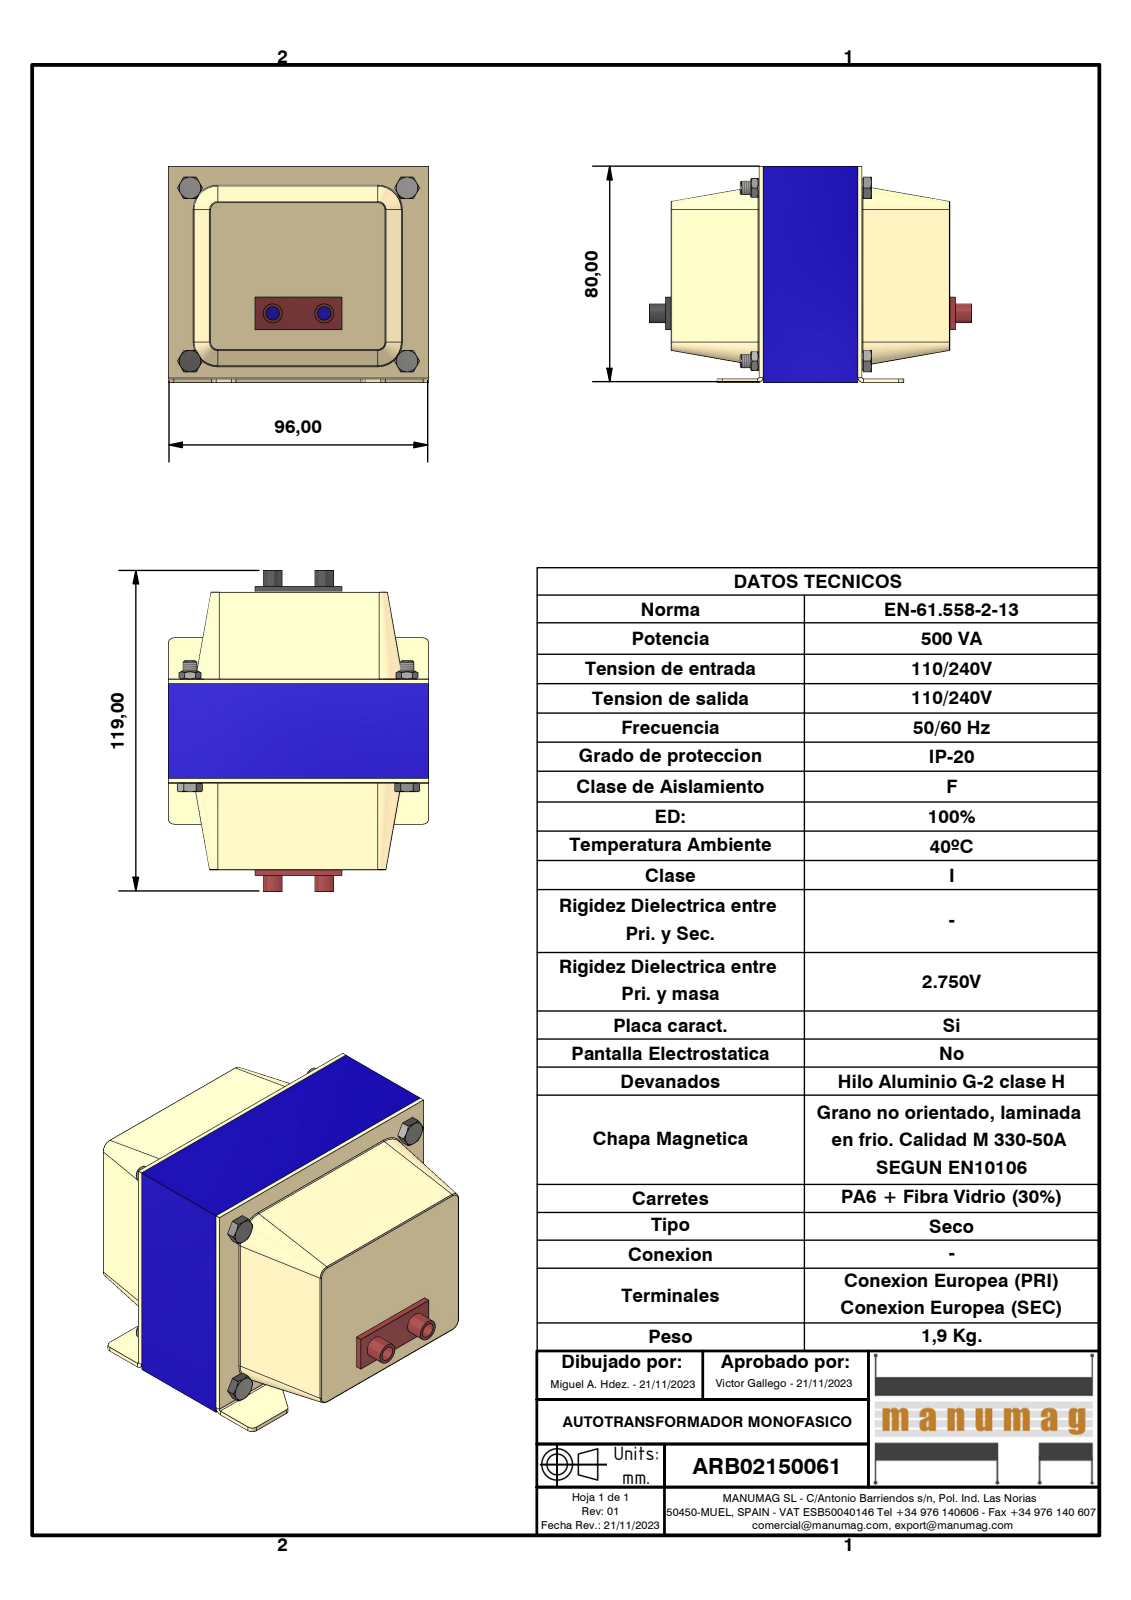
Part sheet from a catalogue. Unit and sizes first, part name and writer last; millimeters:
Units: millimetres
Overall size (bounding box): 119 × 96 × 80
Round holes (diameter × count): ⌀5 ×6, ⌀3.24 ×4, ⌀5.5 ×4
Round bosses / shafts (diameter × count): ⌀6.7 ×4, ⌀4.57 ×4, ⌀7 ×2
Partial cylindrical surfaces — rounded edges, fillets, slot ends (radius × count): R0.38 ×16, R2 ×14, R0.5 ×2
Main face-to-face distances: 1.5, 69, 32.5, 16, 35, 64, 80, 34, 101.5, 67.5
Hole centre spacings: 35.23, 52.55, 55.5, 64, 67.83, 80, 102.45, 19
Volume: 242 489 mm³ · Surface area: 104 307 mm²
Bodies: 13 solids, 310 faces (162 planar, 68 cylindrical, 80 other)
Part name (STEP PRODUCT): ARB02150061; TAPA RC32 RECEPTACULO; Receptaculo Rojo; Receptaculo negro (+3 more)
STEP written by: Autodesk Inventor 2023 (AUTOMOTIVE_DESIGN)
